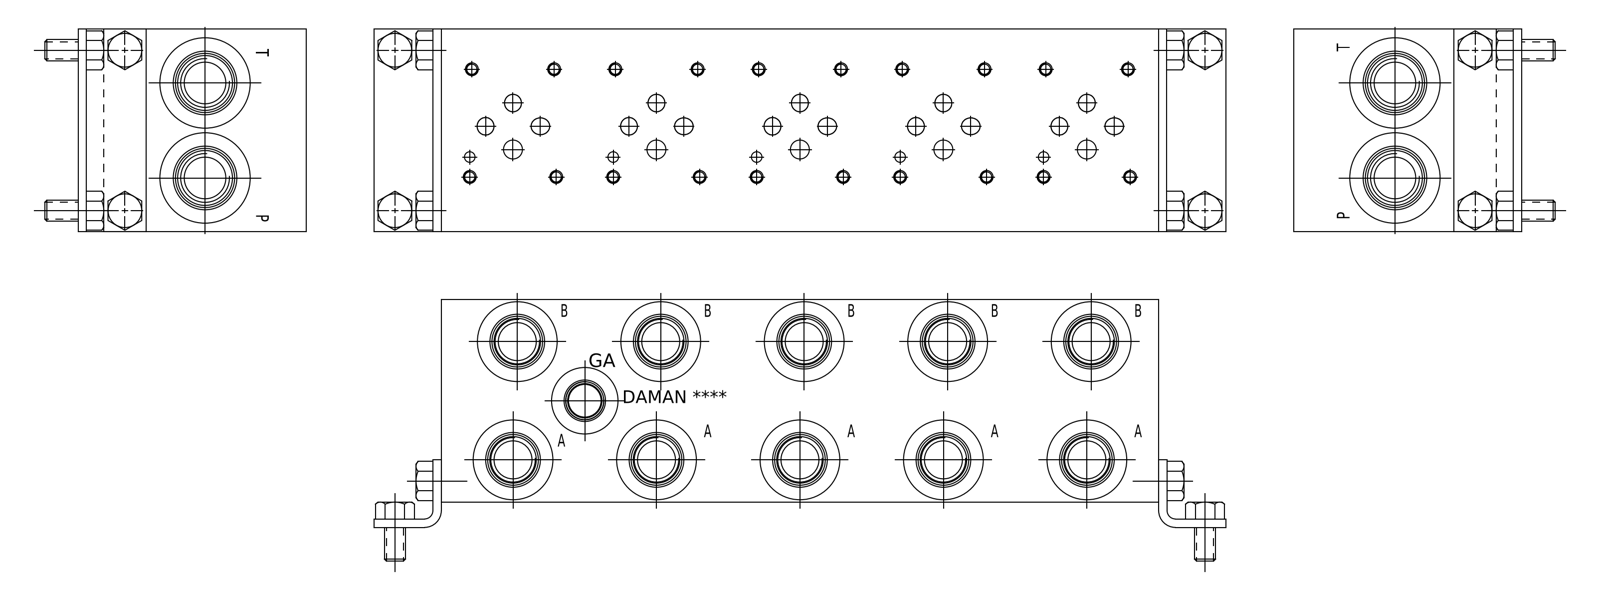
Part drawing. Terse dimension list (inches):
name: Part_AD03S052S_3D
written by: Autodesk Inventor 2019 (AUTOMOTIVE_DESIGN)
unit: in
bodies: 1 solid, 927 faces (449 planar, 151 cylindrical, 327 other)
size: 10.625 × 3 × 3
volume: 88.24 in³; area: 193.2 in²
holes: 20× ⌀0.149, 20× ⌀0.19, 15× ⌀0.25, 10× ⌀0.563, 10× ⌀0.689, 10× ⌀0.75, 10× ⌀0.758, 10× ⌀1.206, 5× ⌀0.156, 5× ⌀0.281, 2× ⌀0.257, 2× ⌀0.312
face distances: 3, 0.031, 2.969, 10.625, 10.594, 10.563, 0.593, 0.562, 2.407, 0.039
hole spacings: 4.25, 2.125, 2.125, 6.375, 6.375, 8.5, 2.233, 3.858
